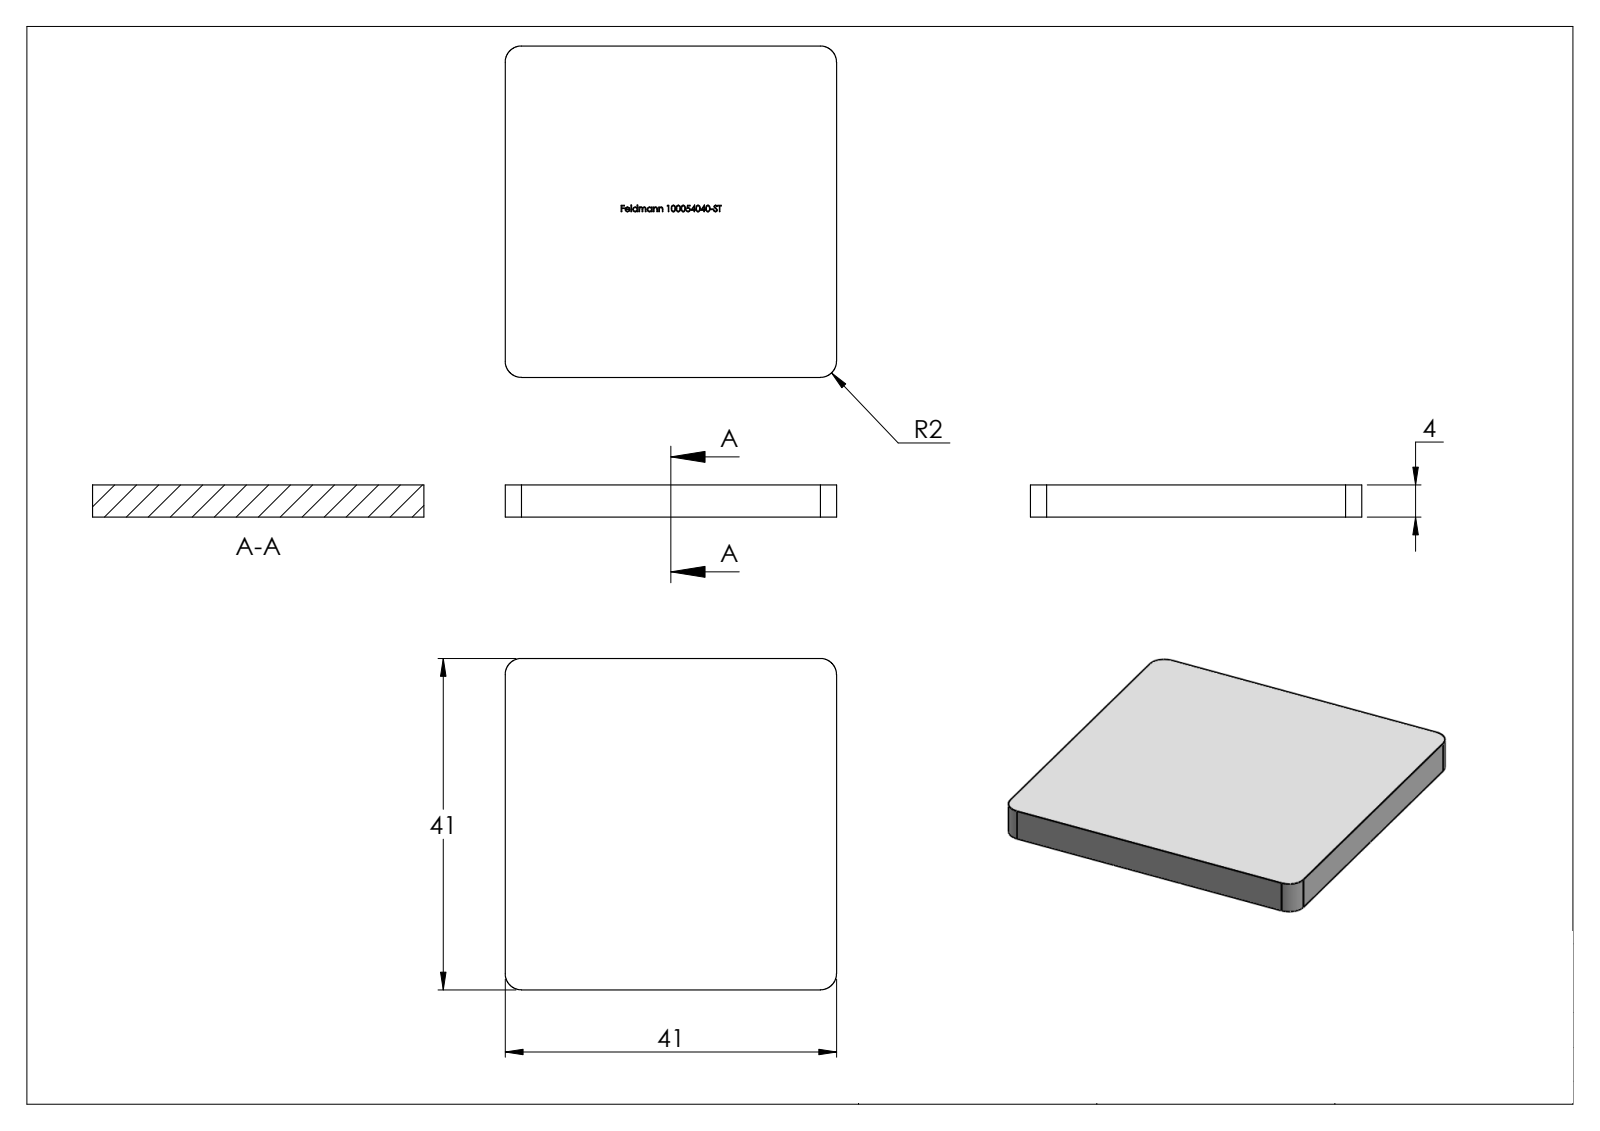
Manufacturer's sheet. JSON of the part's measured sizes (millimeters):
{"part_name": "100054040-ST", "step_written_by": "SolidWorks 2018 (CONFIG_CONTROL_DESIGN)", "units": "millimeters", "bodies": {"solids": 1, "faces": 262, "planar": 142, "cylindrical": 4, "other": 116}, "overall_size": [41, 41, 4], "volume_mm3": 6710, "surface_area_mm2": 4004, "partial_cylinders_radius": [[2, 4]], "face_to_face_distances": [4, 41, 3.9, 20.5, 6.32, 0.53, 1.91, 20.24, 20.76, 4.61]}
